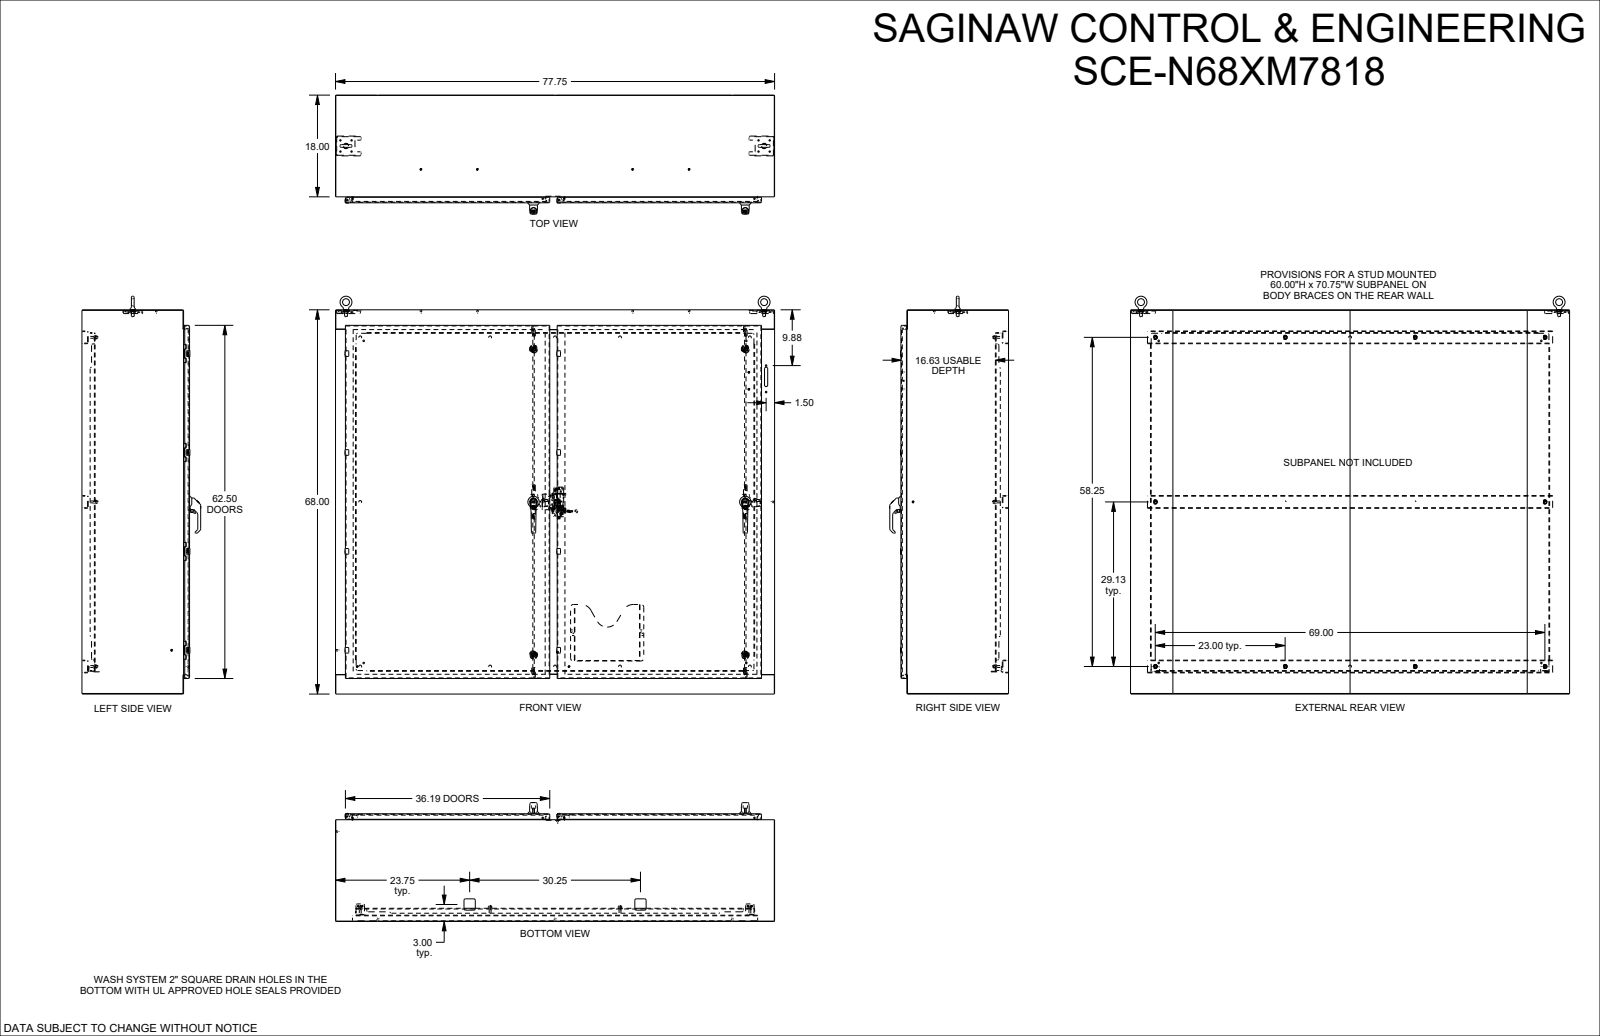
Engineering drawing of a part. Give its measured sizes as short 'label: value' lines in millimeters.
name: SCE-N68XM7818
written by: SolidWorks 2023 (AUTOMOTIVE_DESIGN)
unit: mm
bodies: 46 solids, 7213 faces (3016 planar, 2409 cylindrical, 1788 other)
size: 1974.9 × 1802 × 534.6
volume: 32 410 000 mm³; area: 24 300 000 mm²
holes: 16× ⌀6.2, 14× ⌀6.4, 8× ⌀1, 8× ⌀4.3, 8× ⌀5.2, 8× ⌀5.2, 8× ⌀5.5, 8× ⌀9.5, 8× ⌀9.5, 4× ⌀6.5, 4× ⌀8.7, 4× ⌀8.7
bosses: 24× ⌀4.3, 19× ⌀6.4, 16× ⌀6.1, 10× ⌀5, 4× ⌀35.6, 4× ⌀8.7, 2× ⌀51, 2× ⌀29.8
rounds: 204× R0.8, 162× R0.4, 66× R3.2, 65× R0.5, 57× R1, 52× R1.6, 48× R0.5, 43× R6.4
face distances: 2.6, 481.4, 478.8, 484.1, 454.6, 26.9, 1724.6, 1972.2, 451.9, 29.5
hole spacings: 444.5, 889, 952.5, 807, 25, 35.5, 35.6, 39.3
